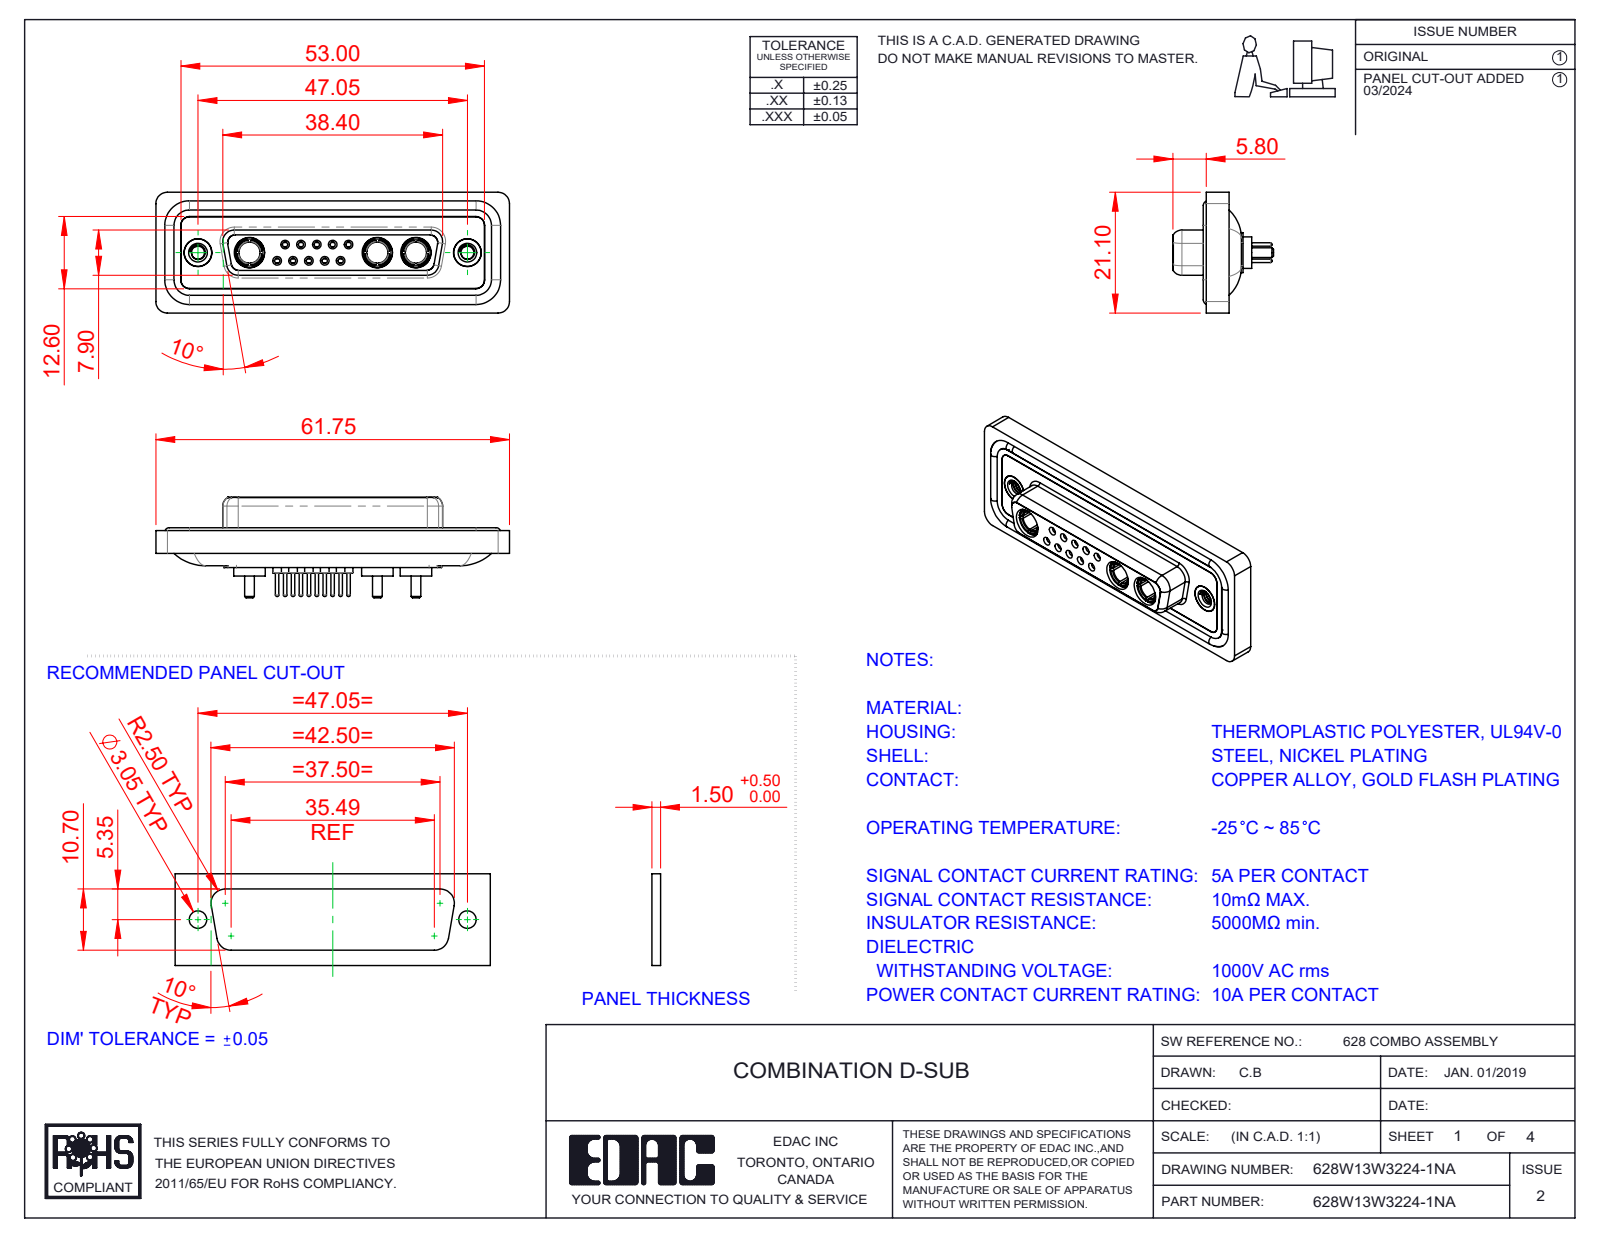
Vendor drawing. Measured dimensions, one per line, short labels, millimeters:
name: 628Combo Contact Row 1_24; 628Combo Housing_13W3; 628Combo Waterproof Housing_25 Contacts; 628Combo Threaded Rivet_A (+5 more)
written by: SolidWorks 2023 (CONFIG_CONTROL_DESIGN)
unit: mm
bodies: 23 solids, 1156 faces (342 planar, 449 cylindrical, 365 other)
size: 61.75 × 21.1 × 17.55
volume: 8 231 mm³; area: 13 668 mm²
holes: 10× ⌀0.9, 10× ⌀1.1, 10× ⌀1.5, 10× ⌀2, 5× ⌀1.6, 5× ⌀1.7, 5× ⌀4.85, 3× ⌀3.7, 3× ⌀5.3, 2× ⌀2.26, 2× ⌀4, 2× ⌀4.05
bosses: 10× ⌀2.2, 10× ⌀0.6, 9× ⌀1.6, 3× ⌀5.5, 3× ⌀5.2, 3× ⌀4.96, 3× ⌀4.75, 3× ⌀3.75
rounds: 22× R1.5, 18× R2, 8× R1.35, 8× R1.6, 4× R0.25, 4× R0.5, 4× R0.6, 4× R0.65
face distances: 0.4, 1.8, 7.45, 5.65, 0.5, 6.6, 7.05, 1.6, 2.9, 1.1
hole spacings: 3.16, 2.77, 5.03, 5.04, 5.54, 8.31, 7.49, 2.76
